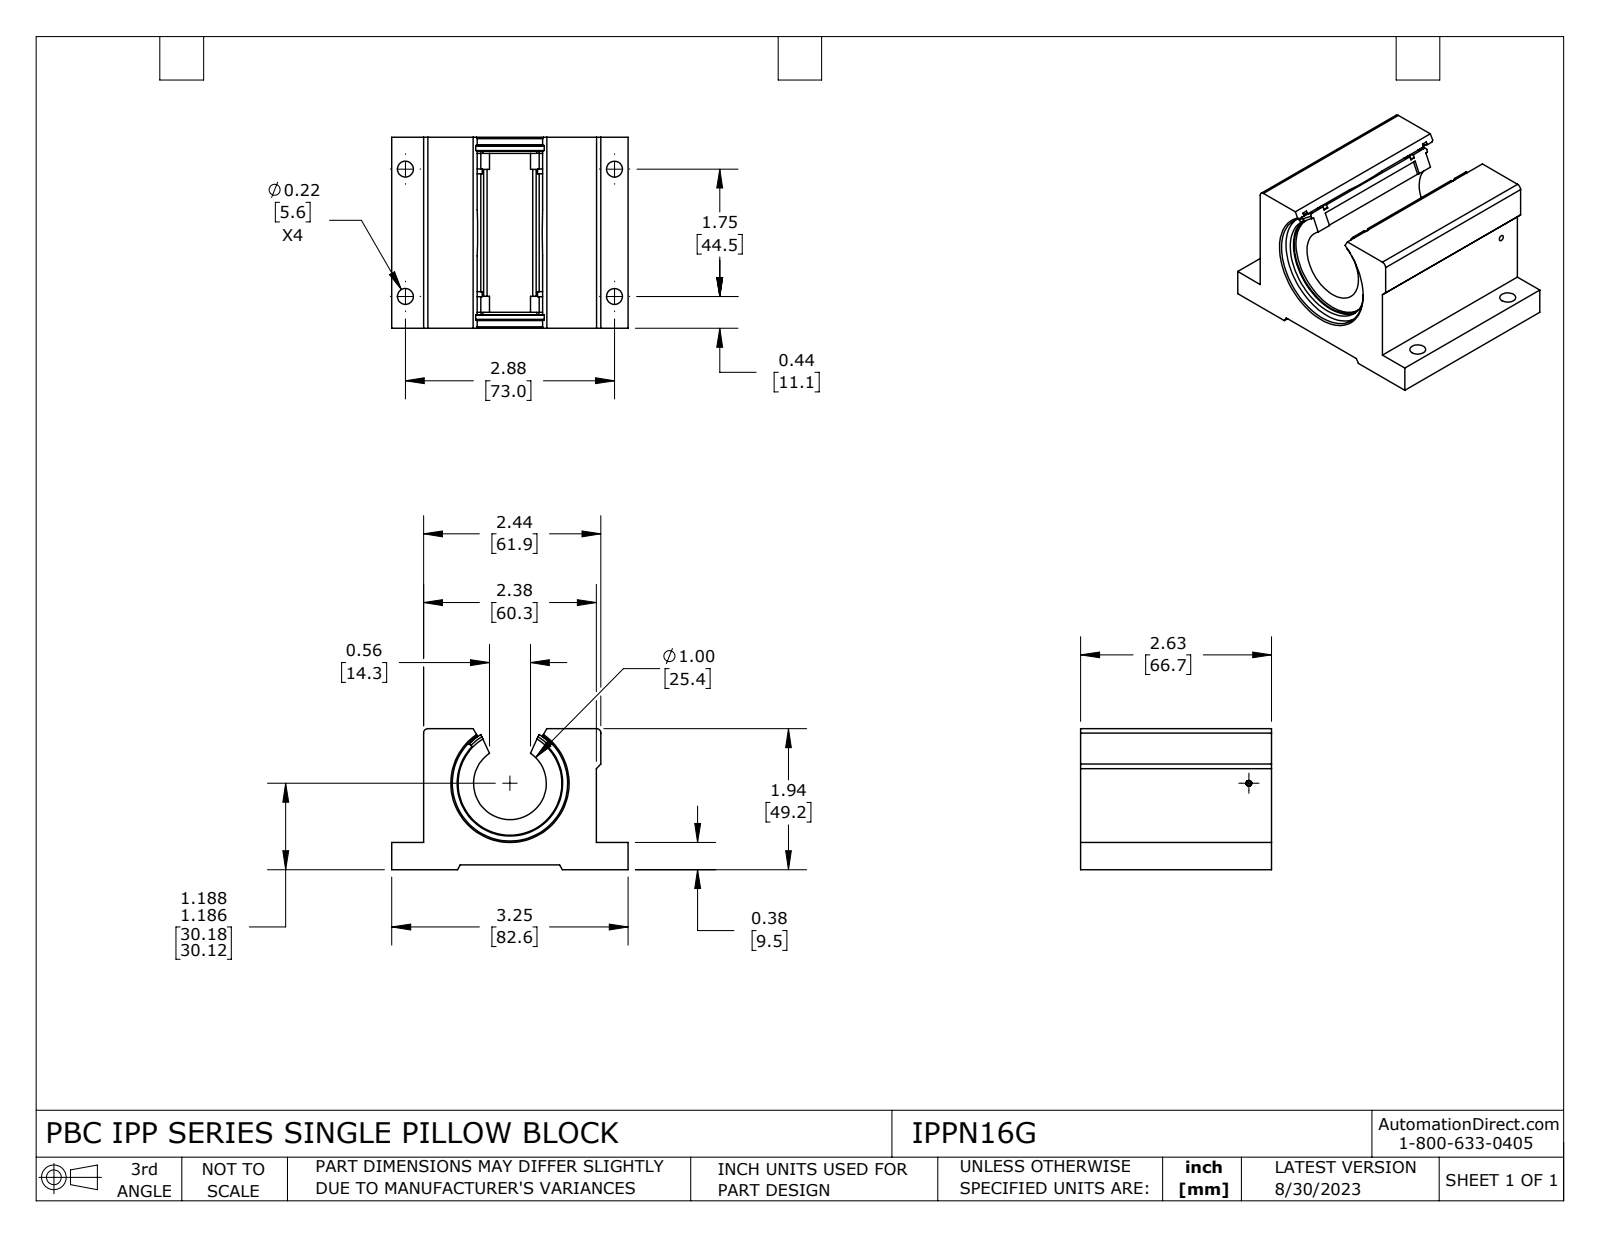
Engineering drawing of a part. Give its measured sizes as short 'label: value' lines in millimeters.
name: IPPN16G
written by: SolidWorks 2021 (CONFIG_CONTROL_DESIGN)
unit: mm
bodies: 5 solids, 157 faces (52 planar, 74 cylindrical, 31 other)
size: 82.6 × 66.7 × 49.2
volume: 156 600 mm³; area: 41 770 mm²
holes: 4× ⌀5.6, 1× ⌀1.4, 1× ⌀2, 1× ⌀3.5, 1× ⌀25.4, 1× ⌀36.2, 1× ⌀40.3, 1× ⌀42.4
bosses: 1× ⌀39.7, 1× ⌀37.3, 1× ⌀2
rounds: 2× R0.8, 2× R1.5, 2× R4.6, 1× R17.4, 1× R18.4, 1× R21.5
face distances: 49.2, 1.7, 47.6, 66.7, 60.3, 9.5, 7.9, 39.7, 11.1, 71.4
hole spacings: 44.5, 73, 85.5
